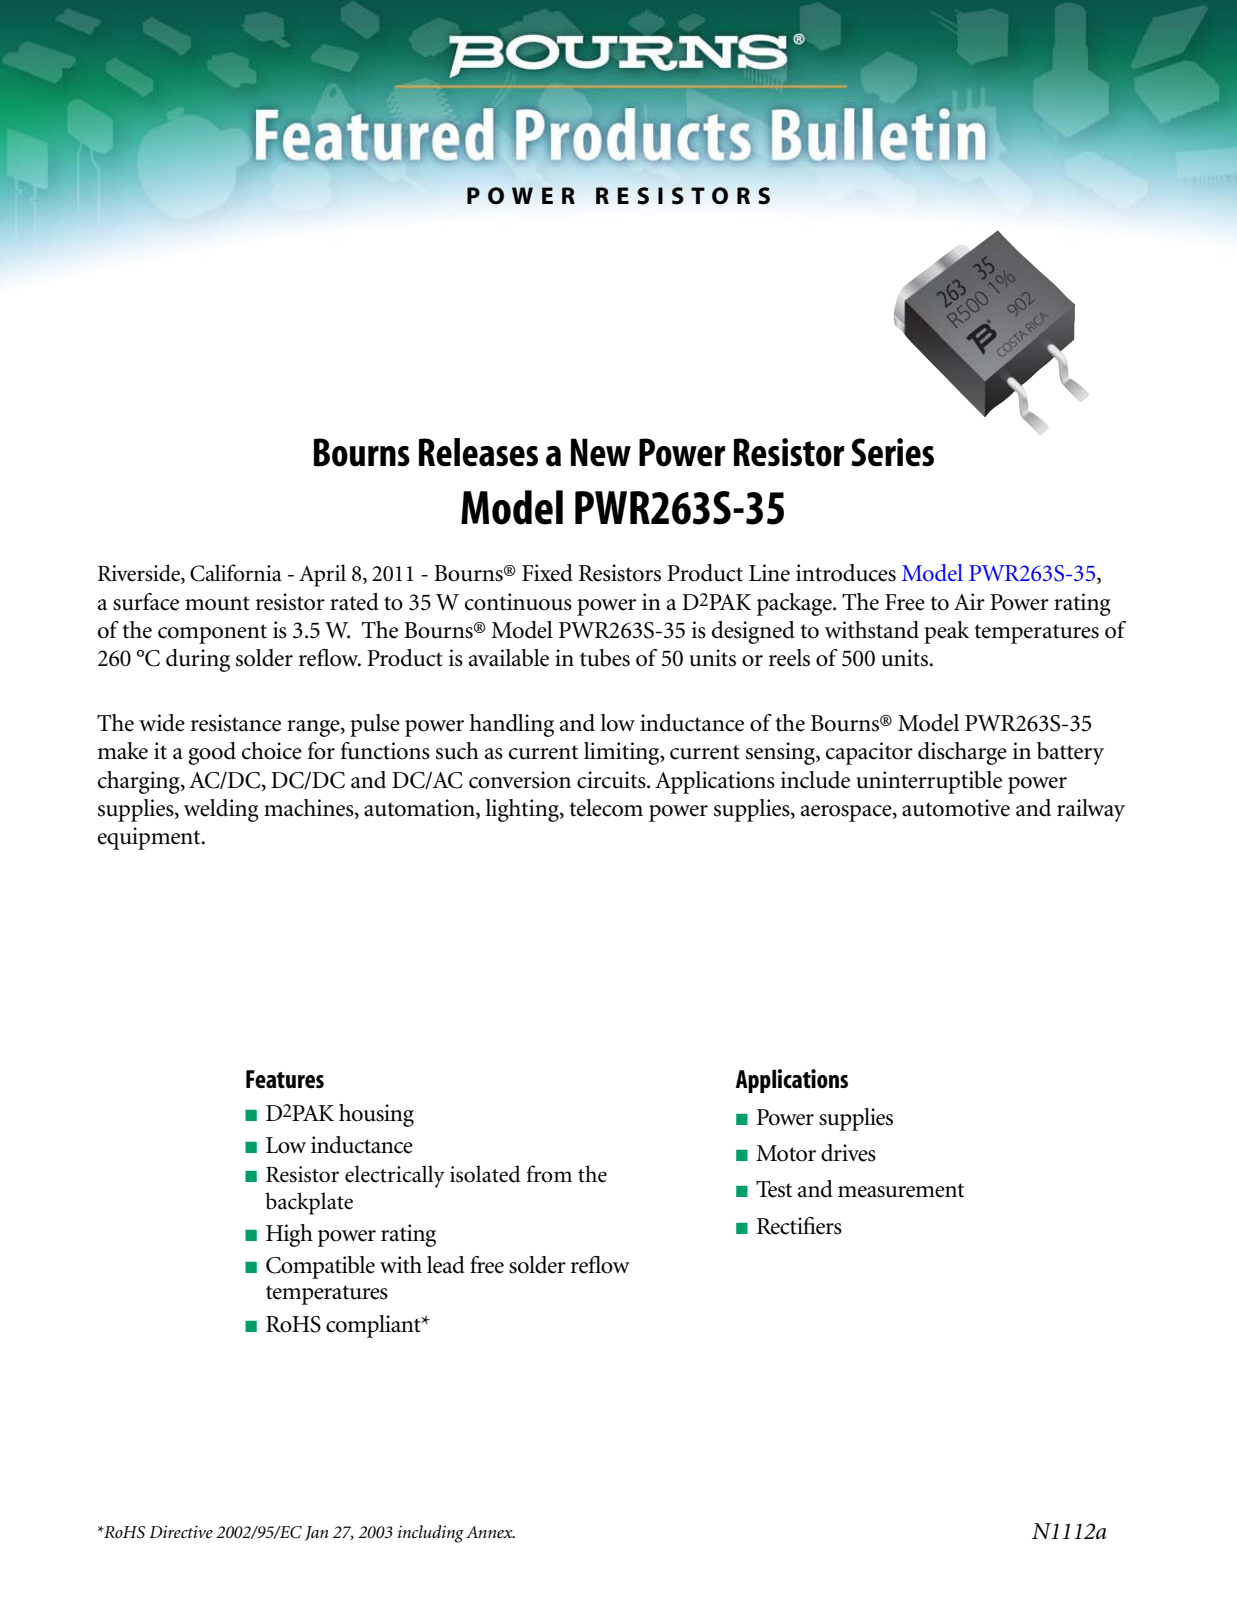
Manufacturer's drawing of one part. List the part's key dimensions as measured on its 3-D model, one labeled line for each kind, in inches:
Part name (STEP PRODUCT): PWR263S-20
STEP written by: PRO/ENGINEER BY PARAMETRIC TECHNOLOGY CORPORATION, 2010100 (CONFIG_CONTROL_DESIGN)
Units: inches
Bodies: 1 solid, 44 faces (36 planar, 8 cylindrical, 0 other)
Overall size (bounding box): 0.606 × 0.398 × 0.177
Volume: 0.026 in³ · Surface area: 0.648 in²
Partial cylindrical surfaces — rounded edges, fillets, slot ends (radius × count): R0.012 ×4
Main face-to-face distances: 0.177, 0.398, 0.346, 0.051, 0.126, 0.409, 0.063, 0.041, 0.167, 0.2
